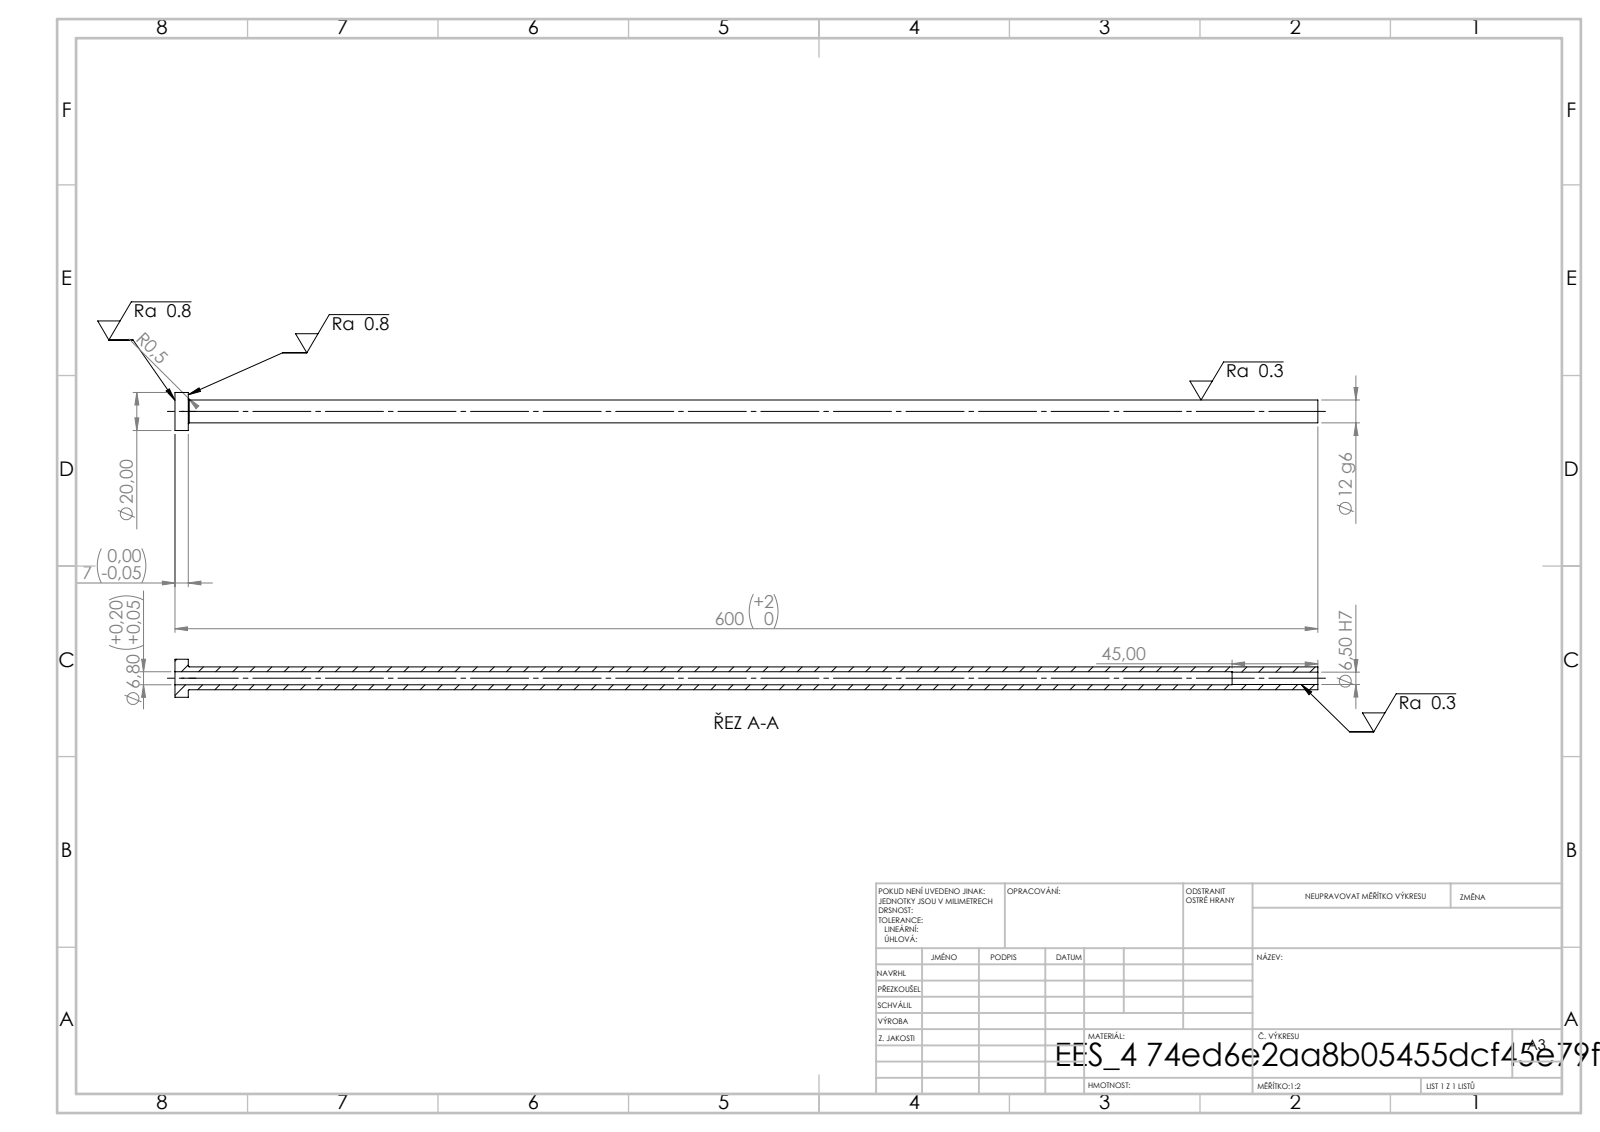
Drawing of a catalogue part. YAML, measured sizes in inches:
step_written_by: "SolidWorks 2019 (CONFIG_CONTROL_DESIGN)"
units: inches
bodies: {solids: 1, faces: 14, planar: 4, cylindrical: 8, other: 2}
overall_size: [23.622, 0.787, 0.787]
volume: 2.906
surface_area: 55.99
round_holes:
  - {diameter: 0.256, count: 1}
  - {diameter: 0.268, count: 1}
round_bosses_or_shafts:
  - {diameter: 0.787, count: 1}
  - {diameter: 0.472, count: 1}
face_to_face_distances: [0.276, 23.622, 23.346, 21.85, 21.575, 1.772]
